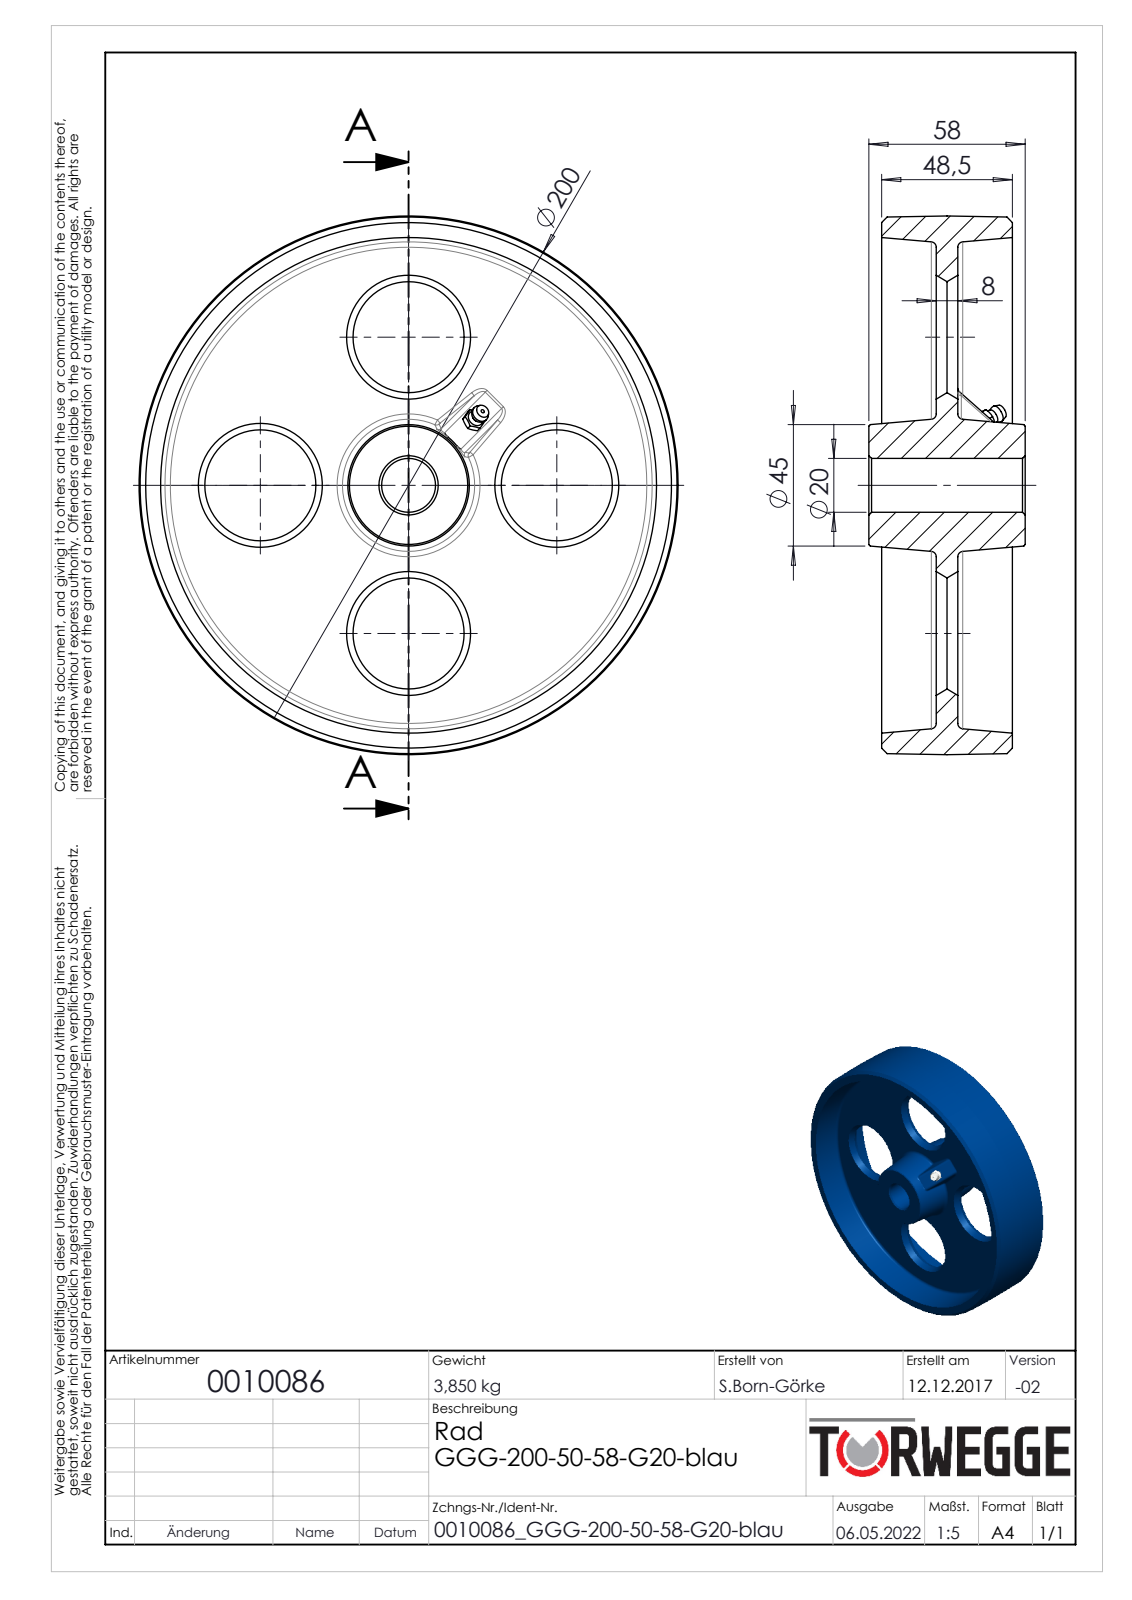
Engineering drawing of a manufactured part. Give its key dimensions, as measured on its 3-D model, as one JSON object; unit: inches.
{"part_name": "0010086", "step_written_by": "SolidWorks 2020 (AUTOMOTIVE_DESIGN)", "units": "inches", "bodies": {"solids": 2, "faces": 101, "planar": 19, "cylindrical": 11, "other": 71}, "overall_size": [7.874, 7.874, 2.283], "volume_in3": 29.5, "surface_area_in2": 175.9, "round_holes": [[0.236, 1], [0.787, 1]], "round_bosses_or_shafts": [[0.236, 1]], "partial_cylinders_radius": [[0.059, 3], [0.079, 2]], "face_to_face_distances": [0.315, 0.797, 1.112, 1.909, 0.187, 0.984, 1.299, 2.096, 2.283, 0.276]}
